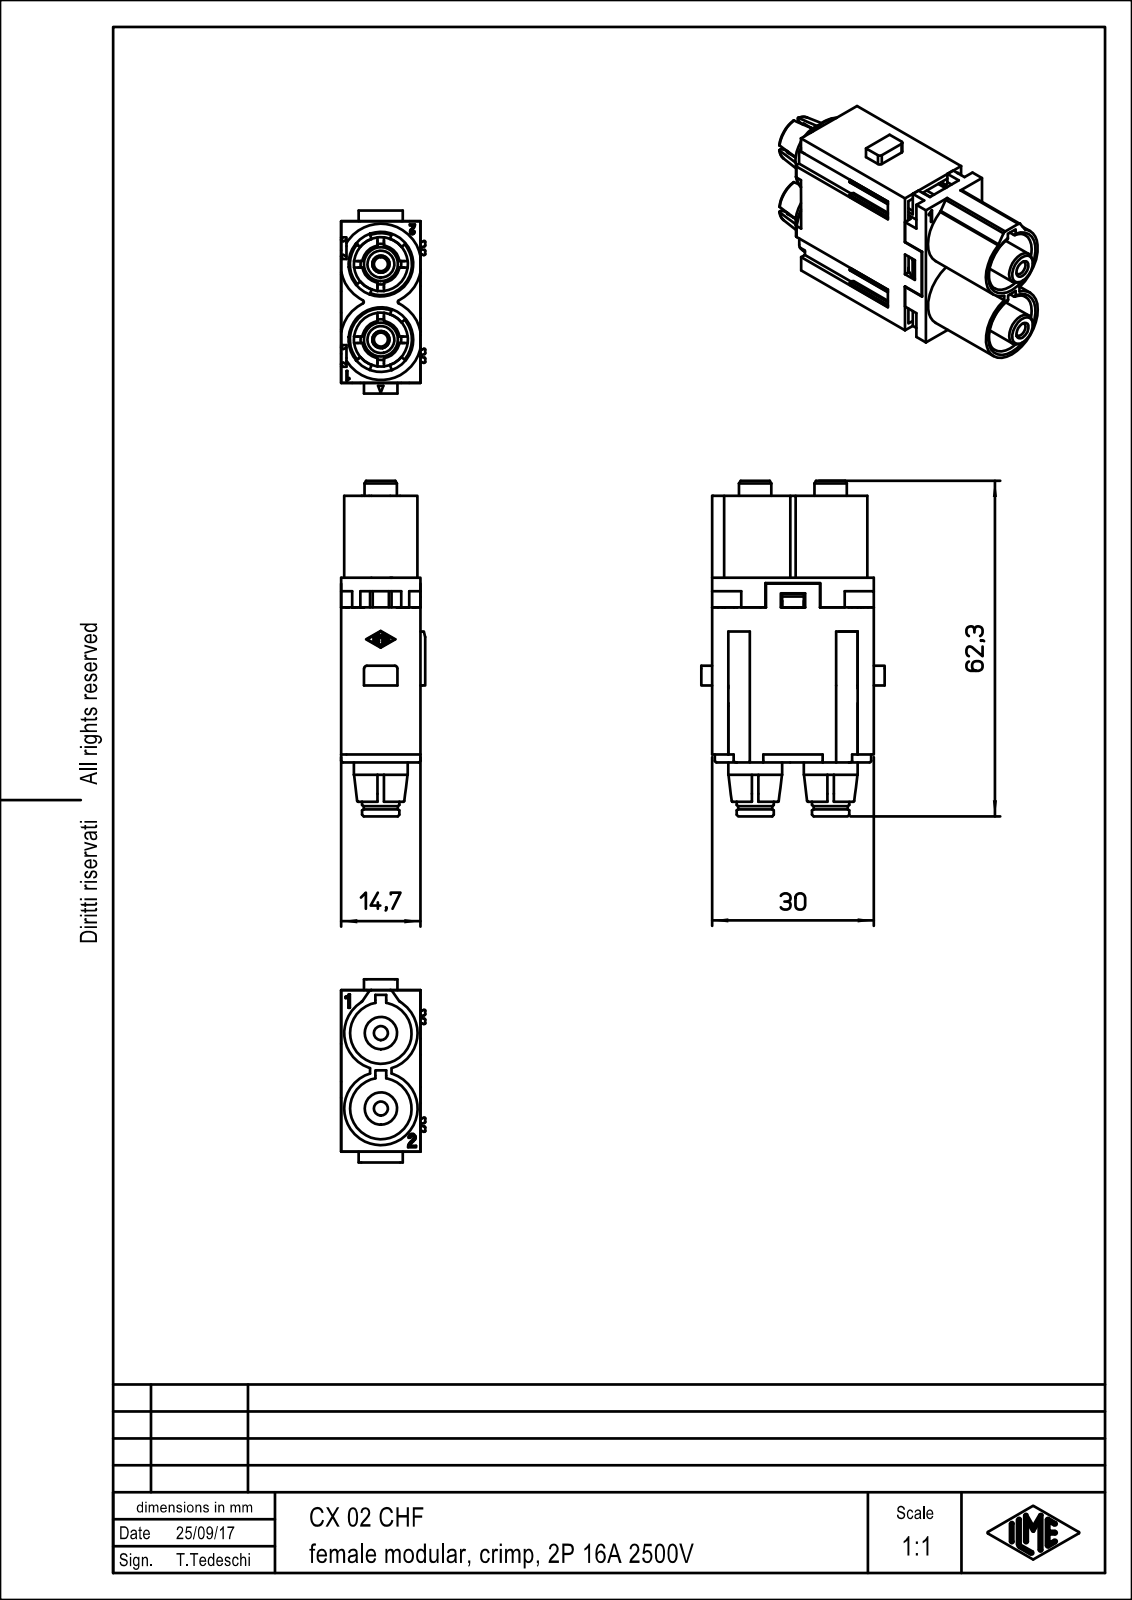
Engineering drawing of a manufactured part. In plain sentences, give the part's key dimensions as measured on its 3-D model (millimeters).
The part is named "CX_02_CHF". Its 3-D file was written by "PTC Creo Elements/Direct Modeling 19.0E 27-Jun-2016 (C) Parametric Technology GmbH (AUTOMOTIVE_DESIGN)". It is 1 solid with 522 faces: 357 planar, 86 cylindrical and 79 other. Overall it measures 62.3 by 34 by 15.6 millimeters. Its volume is 16 027 cubic millimeters and its surface area 12 428 square millimeters. Round holes: 2 of diameter 2.6, 2 of diameter 3.2, 2 of diameter 4.7, 2 of diameter 5, 2 of diameter 7, 2 of diameter 11.3, 2 of diameter 12, 1 of diameter 13.6. Round bosses or shafts: 2 of diameter 11.5, 2 of diameter 11.4, 2 of diameter 7.55, 2 of diameter 6.9, 2 of diameter 6.3, 2 of diameter 6. Partial cylindrical surfaces (rounded edges, fillets, slot ends): 8 of radius 0.5, 5 of radius 0.1, 4 of radius 0.3, 2 of radius 7.5, 1 of radius 6.8. The main face-to-face distances are 14.7, 30, 1, 1.5, 7.3, 4, 13.7, 32.8, 8.3, 4.4. The hole center spacings are 14.
